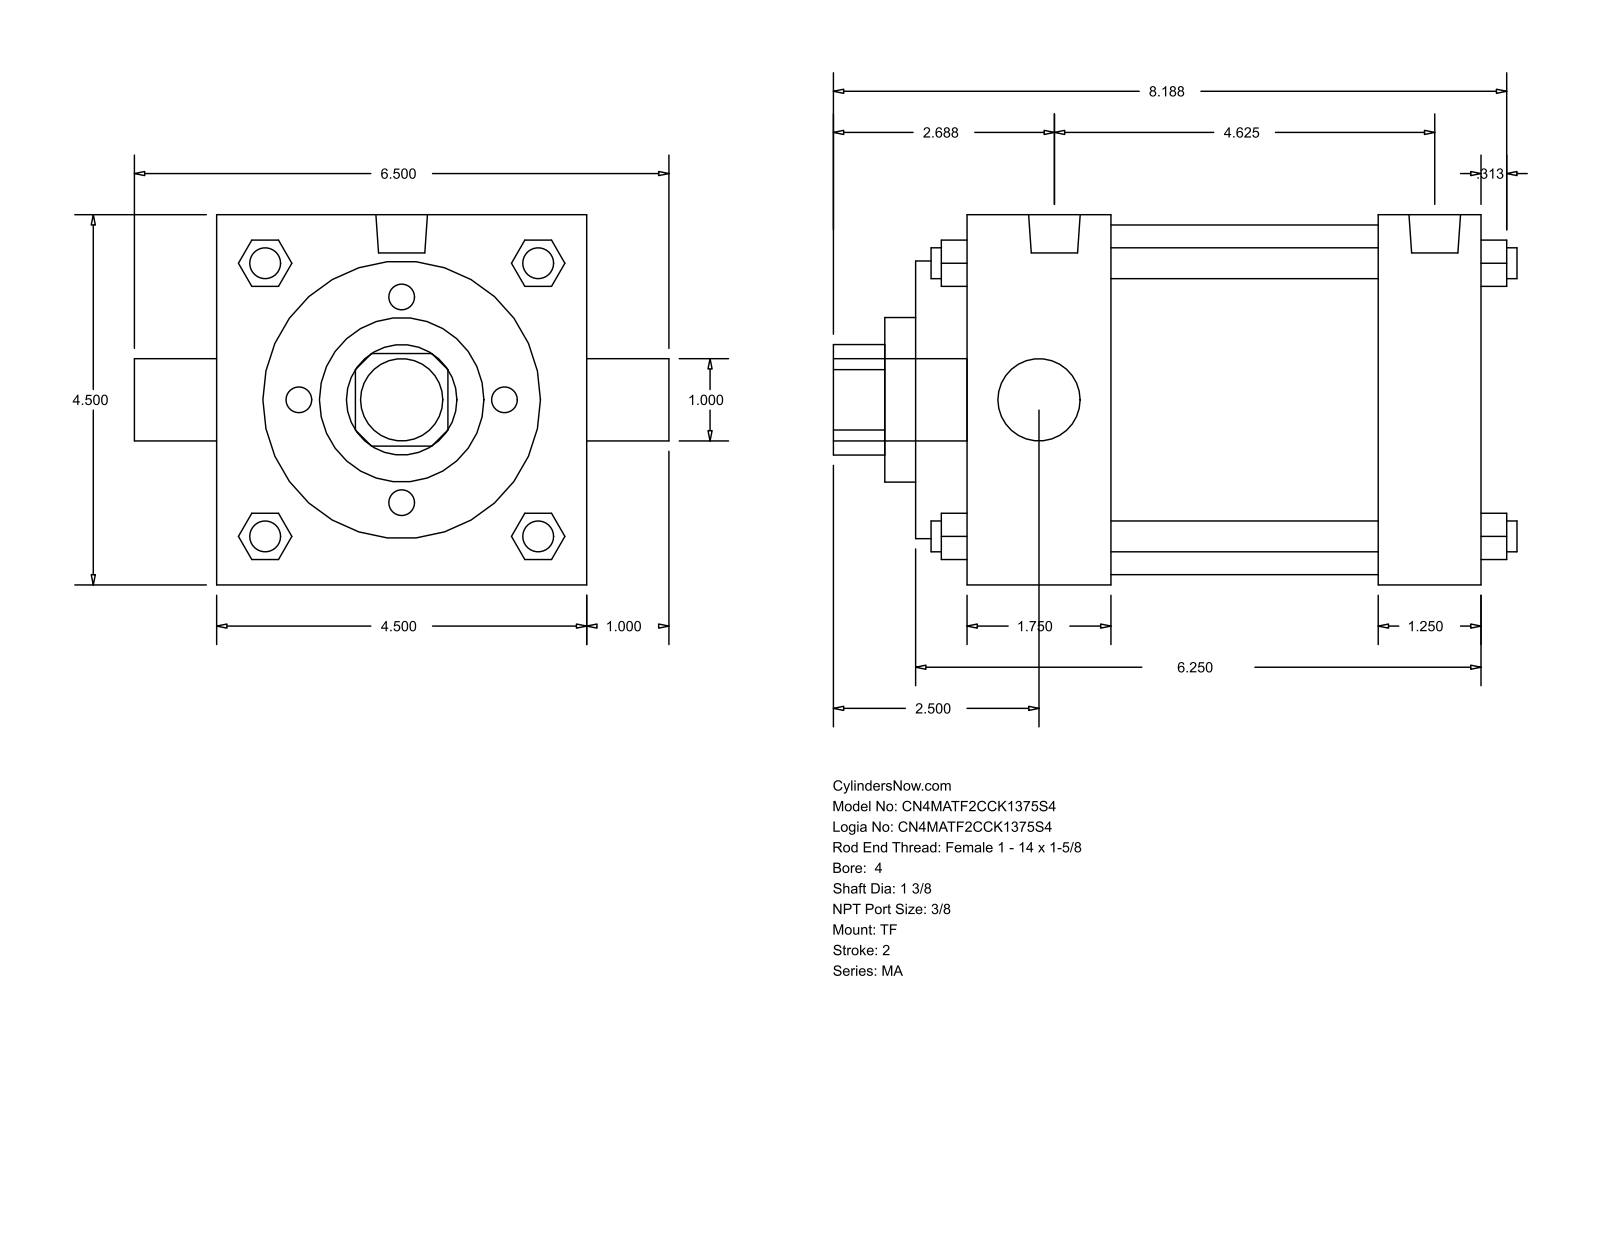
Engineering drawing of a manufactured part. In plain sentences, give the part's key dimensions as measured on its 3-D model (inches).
The part is named "MA_TF__0400_1.375". Its 3-D file was written by "GSSL Pune (CONFIG_CONTROL_DESIGN)". It is 0 solids with 122 faces: 93 planar, 29 cylindrical and 0 other. Overall it measures 8.313 by 6.5 by 4.5 inches. Round holes: 1 of diameter 1, 1 of diameter 1.375, 1 of diameter 2, 1 of diameter 3.375, 1 of diameter 4.25. Round bosses or shafts: 4 of diameter 0.375, 3 of diameter 0.437, 2 of diameter 0.627, 1 of diameter 1. Partial cylindrical surfaces (rounded edges, fillets, slot ends): 1 of radius 0.672. The main face-to-face distances are 4.5, 6.25, 0.625, 6.875, 5.625, 5, 1.25, 2.375, 1.75, 3.25.
